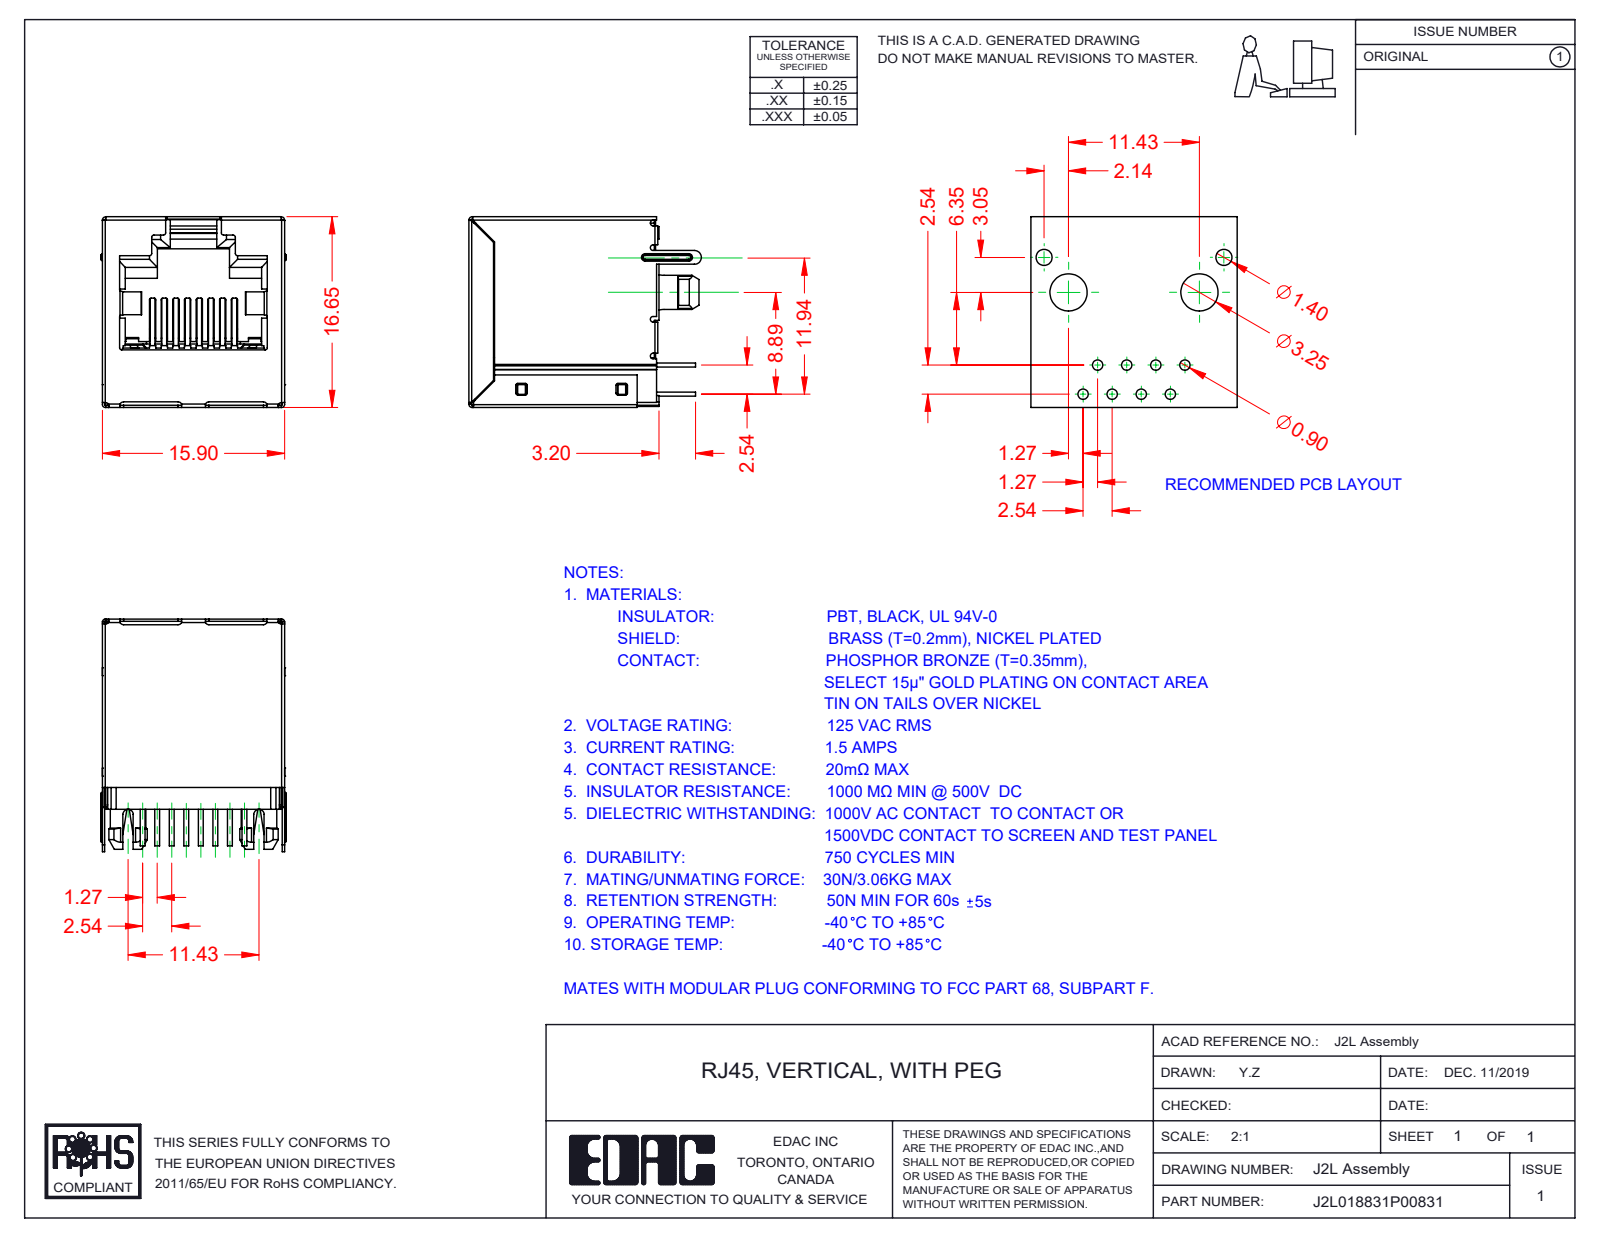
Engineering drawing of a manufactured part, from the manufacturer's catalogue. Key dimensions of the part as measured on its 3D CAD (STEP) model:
Part name (STEP PRODUCT): 2L Insulator; 2L Mylar Tape; 2L Shield; 2L Contact Lock (+2 more)
STEP written by: SolidWorks 2016 (CONFIG_CONTROL_DESIGN)
Units: millimetres
Bodies: 12 solids, 1131 faces (784 planar, 284 cylindrical, 63 other)
Overall size (bounding box): 20.3 × 16.65 × 16.2
Volume: 2 735 mm³ · Surface area: 6 843 mm²
Round bosses / shafts (diameter × count): ⌀3.1 ×2, ⌀1.1 ×2
Partial cylindrical surfaces — rounded edges, fillets, slot ends (radius × count): R0.15 ×64, R0.25 ×20, R0.2 ×16, R0.3 ×14, R0.35 ×9, R0.1 ×8, R0.28 ×4, R0.5 ×3
Main face-to-face distances: 15.45, 15.7, 16.45, 16.2, 16.4, 15.65, 16.3, 16.25, 15.9, 15.5
